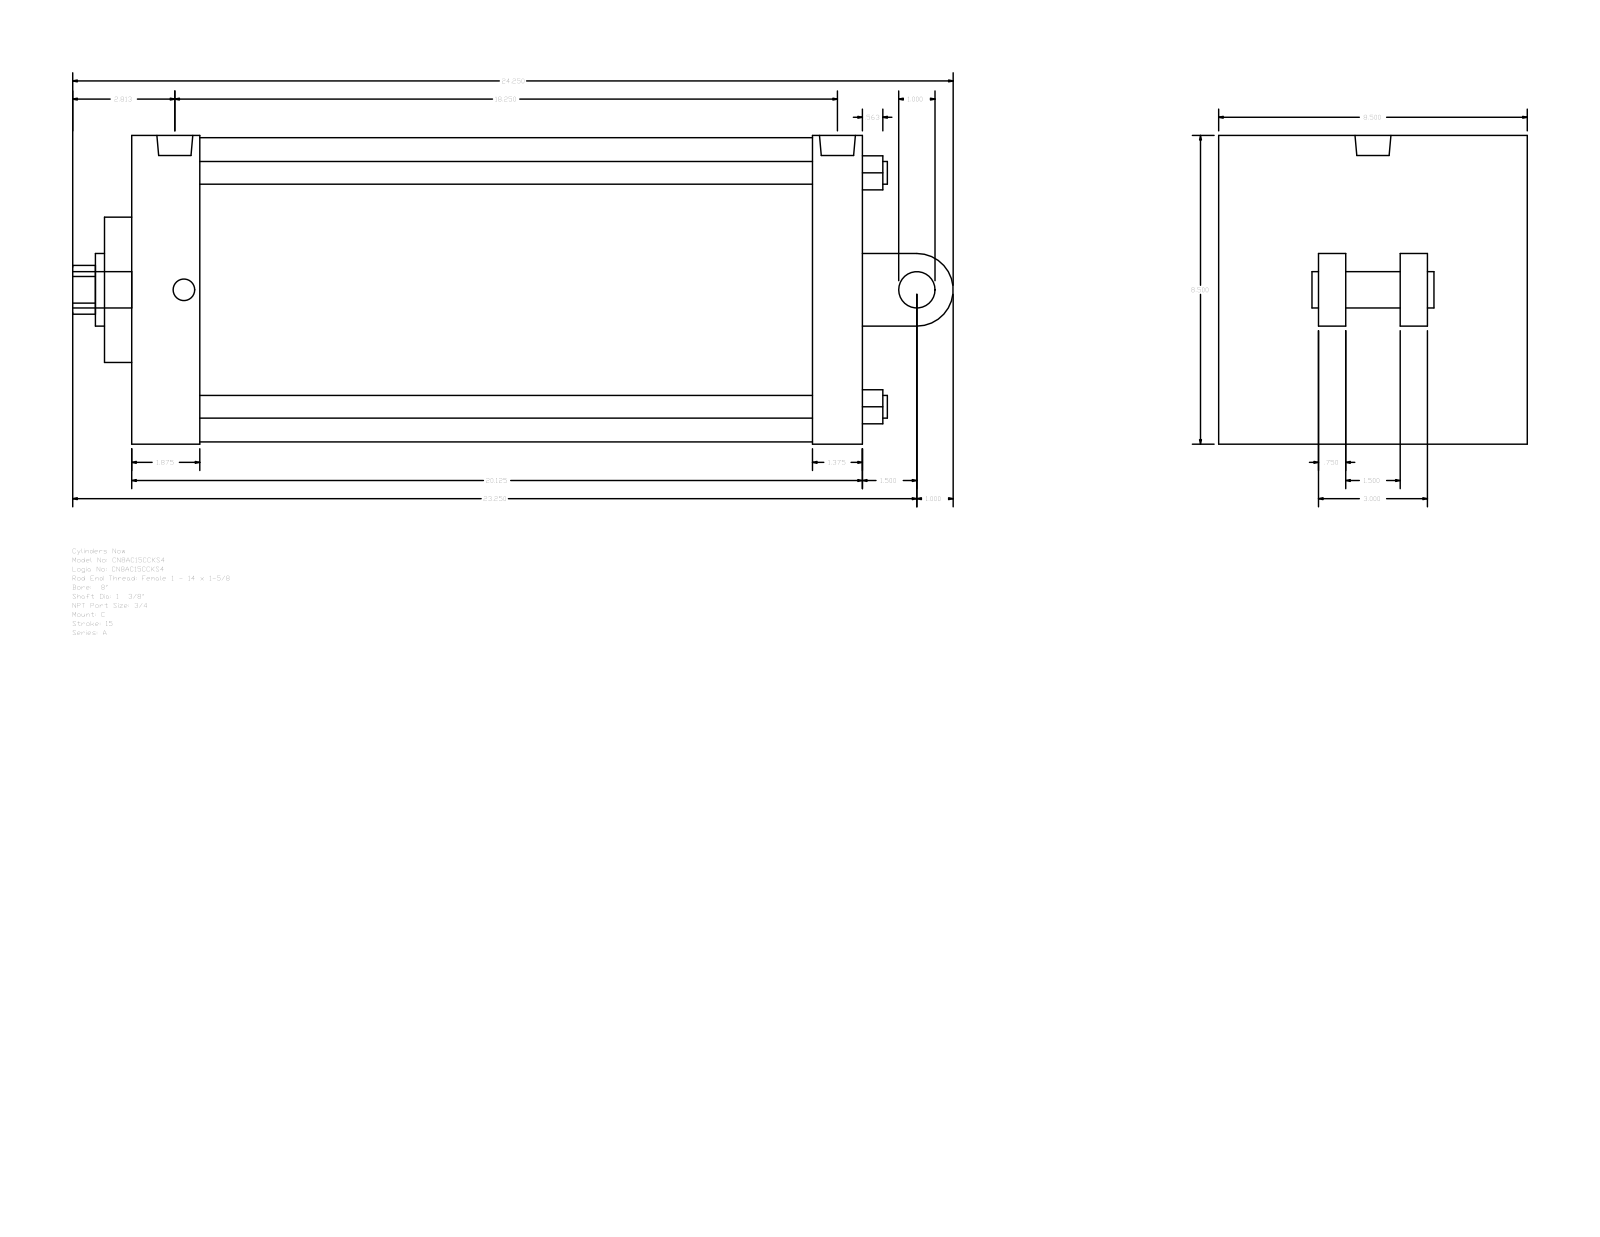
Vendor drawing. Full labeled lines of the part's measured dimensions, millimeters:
Part name (STEP PRODUCT): A_C__0800_1.375
STEP written by: GSSL Pune (CONFIG_CONTROL_DESIGN)
Units: millimetres
Bodies: 0 solids, 104 faces (75 planar, 29 cylindrical, 0 other)
Overall size (bounding box): 615.95 × 215.9 × 215.9
Round holes (diameter × count): ⌀15.88 ×4, ⌀15.08 ×2, ⌀25.12 ×1, ⌀34.92 ×1, ⌀50.8 ×1, ⌀212.72 ×1
Round bosses / shafts (diameter × count): ⌀25.4 ×2, ⌀15.08 ×2, ⌀25.12 ×1
Partial cylindrical surfaces — rounded edges, fillets, slot ends (radius × count): R17.06 ×1, R25.4 ×1
Main face-to-face distances: 511.18, 215.9, 57.15, 47.63, 463.55, 476.25, 428.62, 34.93, 88.9, 69.85
Hole centre spacings: 115.67, 163.58, 231.34, 6.35
